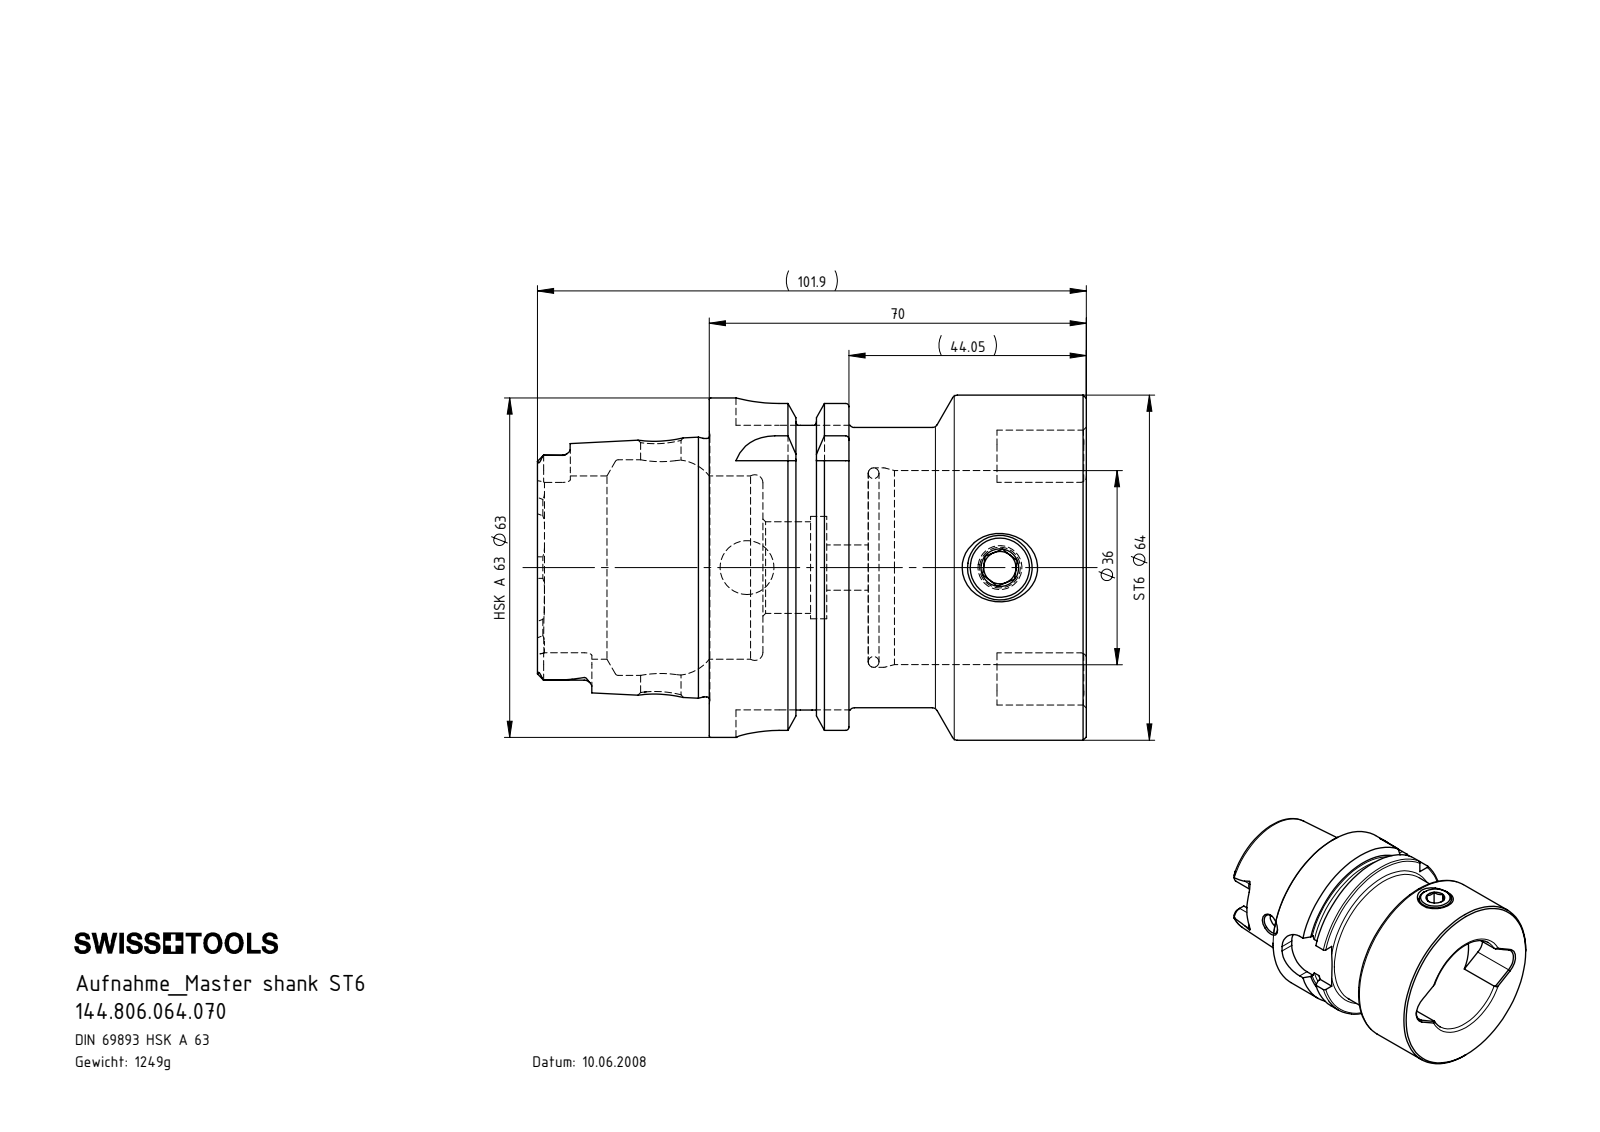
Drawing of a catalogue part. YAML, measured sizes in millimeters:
part_name: "144.806.064.070; DIN 3771 - 33x2; ST6-ER1.001.018_A; HA6-ST6.K01.070_B_Fertigbearbeitung"
step_written_by: "SolidWorks 2017 (AUTOMOTIVE_DESIGN)"
units: millimeters
bodies: {solids: 3, faces: 236, planar: 70, cylindrical: 60, other: 106}
overall_size: [101.9, 64, 64]
volume: 159466
surface_area: 38845
round_holes:
  - {diameter: 6, count: 1}
  - {diameter: 7.5, count: 1}
  - {diameter: 8.4, count: 1}
  - {diameter: 10, count: 1}
  - {diameter: 11, count: 1}
  - {diameter: 17, count: 1}
  - {diameter: 19, count: 1}
  - {diameter: 34, count: 1}
  - {diameter: 36, count: 1}
  - {diameter: 37, count: 1}
  - {diameter: 40, count: 1}
round_bosses_or_shafts:
  - {diameter: 64, count: 1}
  - {diameter: 63, count: 1}
  - {diameter: 54.95, count: 1}
  - {diameter: 52, count: 1}
  - {diameter: 47.94, count: 1}
  - {diameter: 12, count: 1}
partial_cylinders:
  - {radius: 1.4, count: 6}
  - {radius: 2.88, count: 4}
  - {radius: 8, count: 4}
  - {radius: 5.2, count: 2}
face_to_face_distances: [70, 29.5, 40.5, 25.95, 3.55, 44.05, 16, 9.95, 19.55, 60.05]
hole_center_spacings: [46.95]
